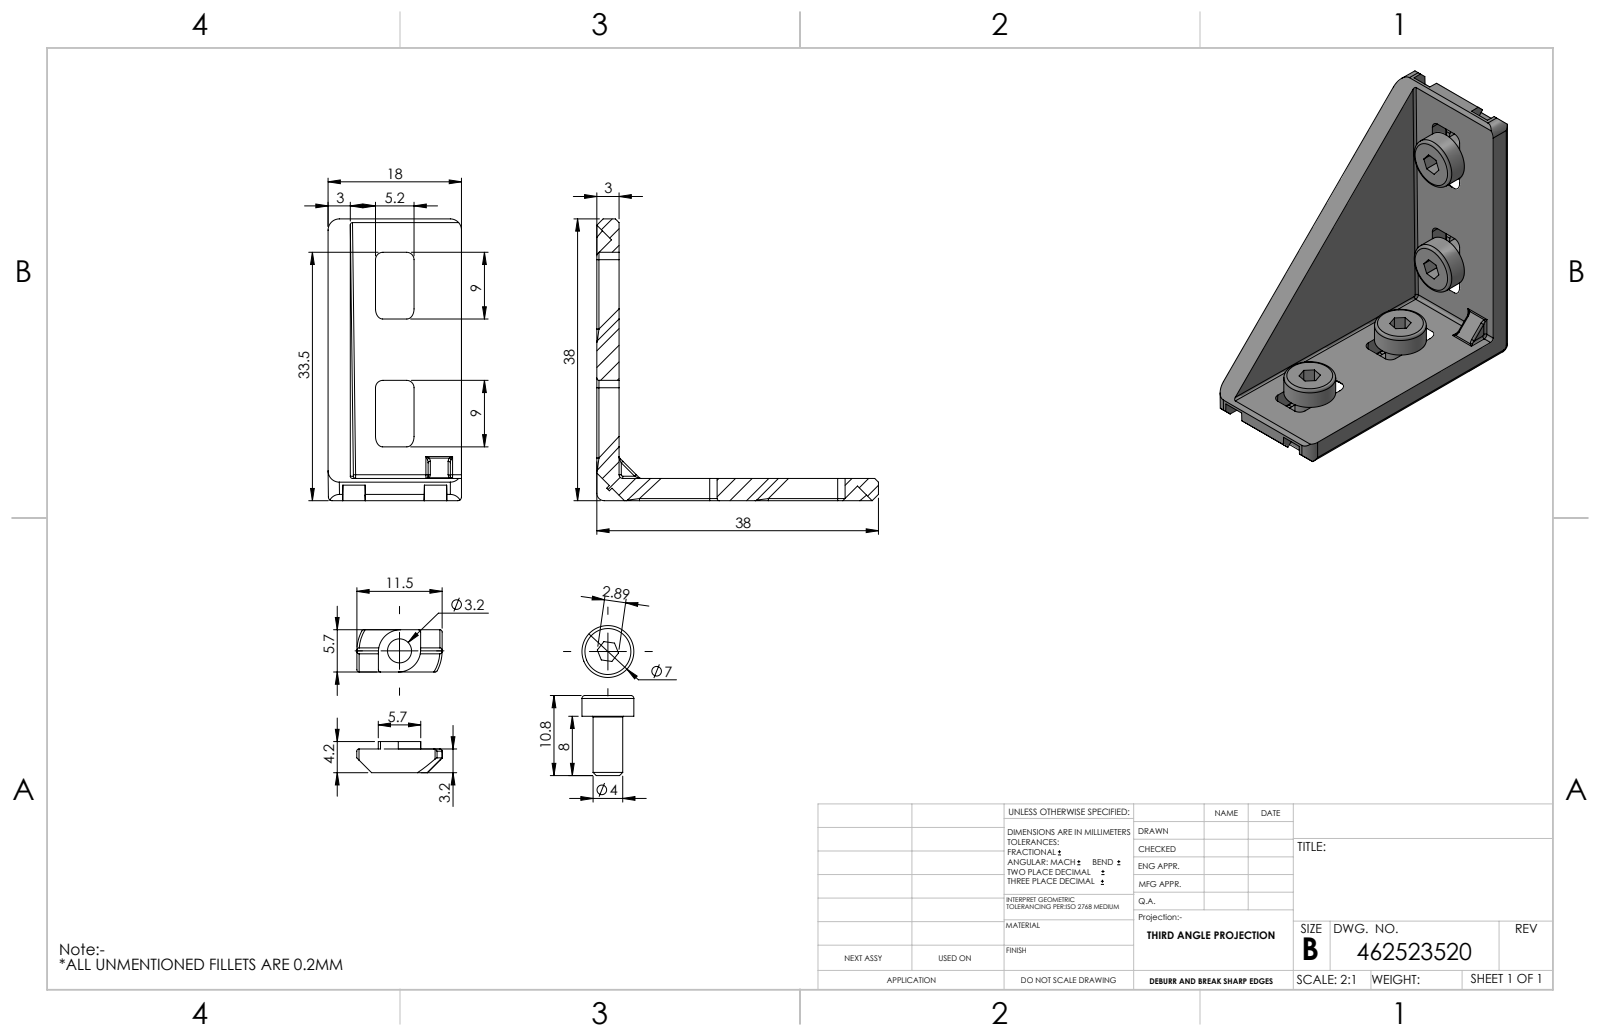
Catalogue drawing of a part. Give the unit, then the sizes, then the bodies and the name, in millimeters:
Units: millimetres
Overall size (bounding box): 43 × 43 × 18
Round holes (diameter × count): ⌀3.24 ×4
Round bosses / shafts (diameter × count): ⌀7 ×4, ⌀4 ×4
Partial cylindrical surfaces — rounded edges, fillets, slot ends (radius × count): R0.3 ×50, R1 ×17, R3 ×8, R0.5 ×5, R1.5 ×4, R5.75 ×4
Main face-to-face distances: 3, 4.5, 5.7, 2.8, 4.7, 7.7, 17.3, 3.5, 1.5, 3.2
Hole centre spacings: 17.3
Volume: 6 313 mm³ · Surface area: 6 201 mm²
Bodies: 9 solids, 347 faces (170 planar, 112 cylindrical, 65 other)
Part name (STEP PRODUCT): 462523517 Winkel 20x40; DIN 7984 - M4 x 8; Syskomp 462523135 Hammermutter N6 M4 verzinkt; 462523520 Winkel 20x40 inkl Bef
STEP written by: Autodesk Inventor 2014 (AUTOMOTIVE_DESIGN)
